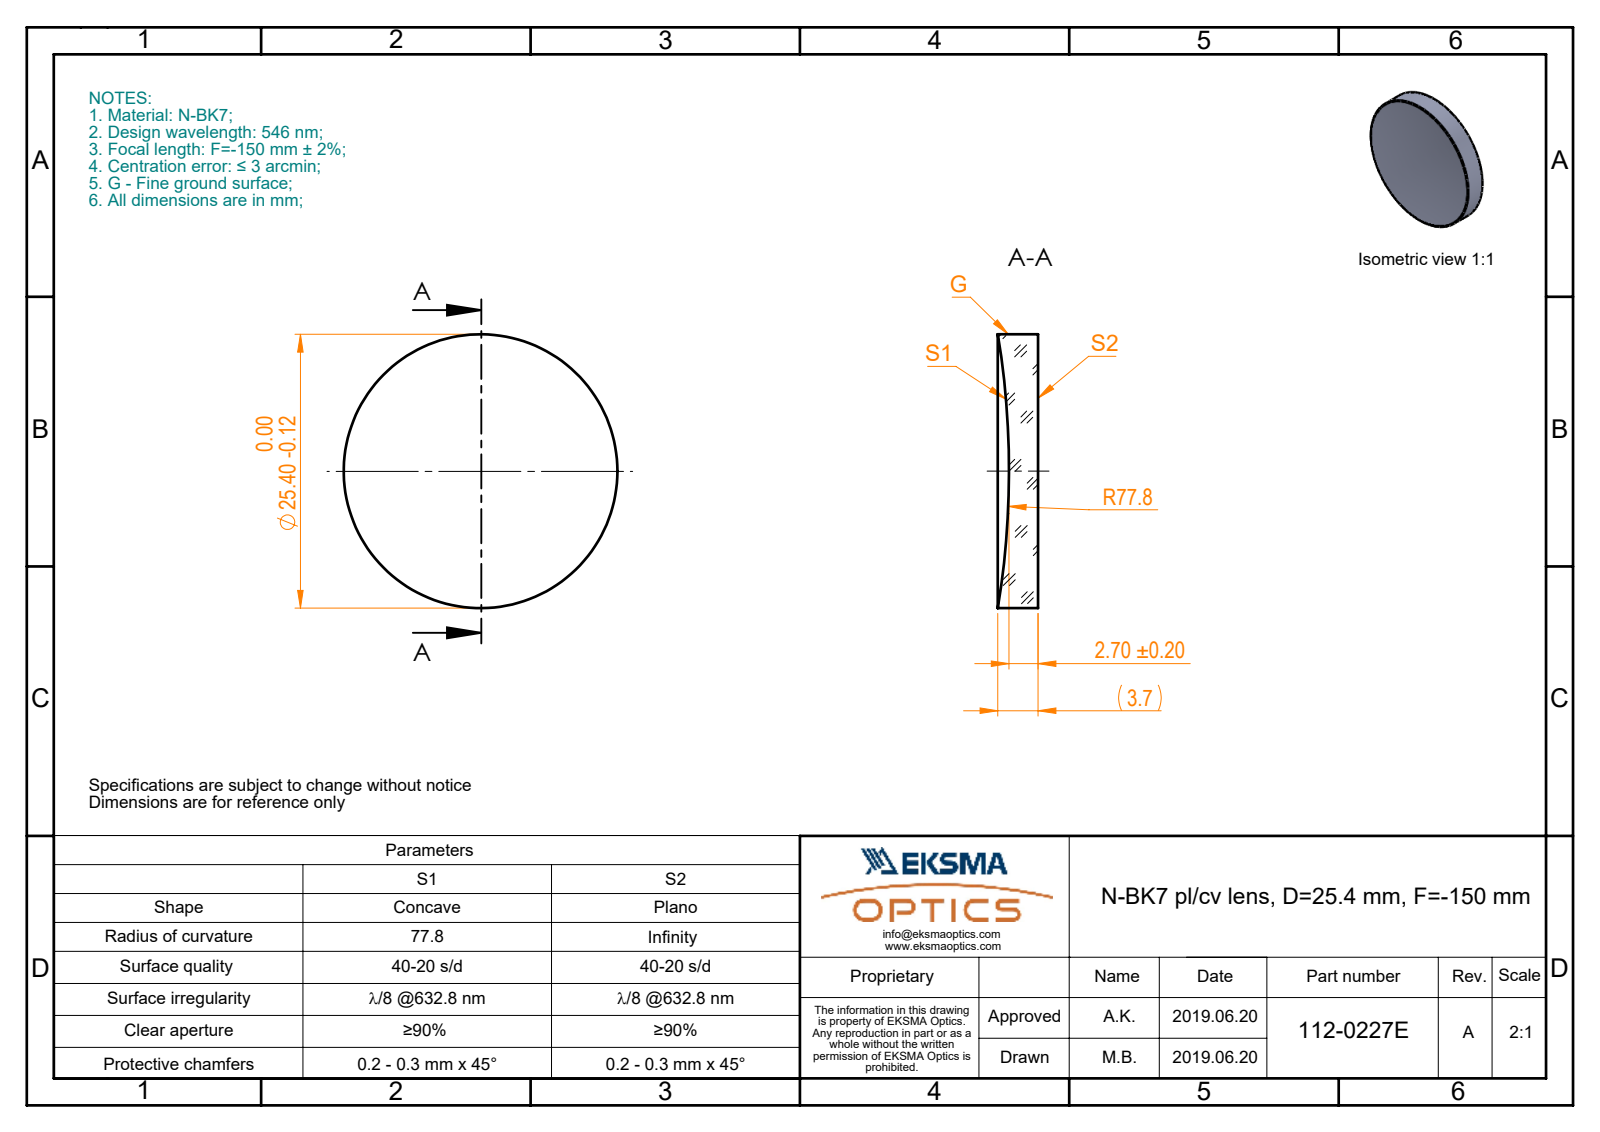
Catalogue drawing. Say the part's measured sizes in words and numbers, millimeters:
The part is named "112-0227E BK7 pl-cv 25.4 F-150". Its 3-D file was written by "SolidWorks 2017 (CONFIG_CONTROL_DESIGN)". It is 1 solid with 5 faces: 1 planar, 2 cylindrical and 2 other. Overall it measures 25.4 by 25.4 by 3.74 millimeters. Its volume is 1 632 cubic millimeters and its surface area 1 316 square millimeters. Round bosses or shafts: 1 of diameter 25.4.
